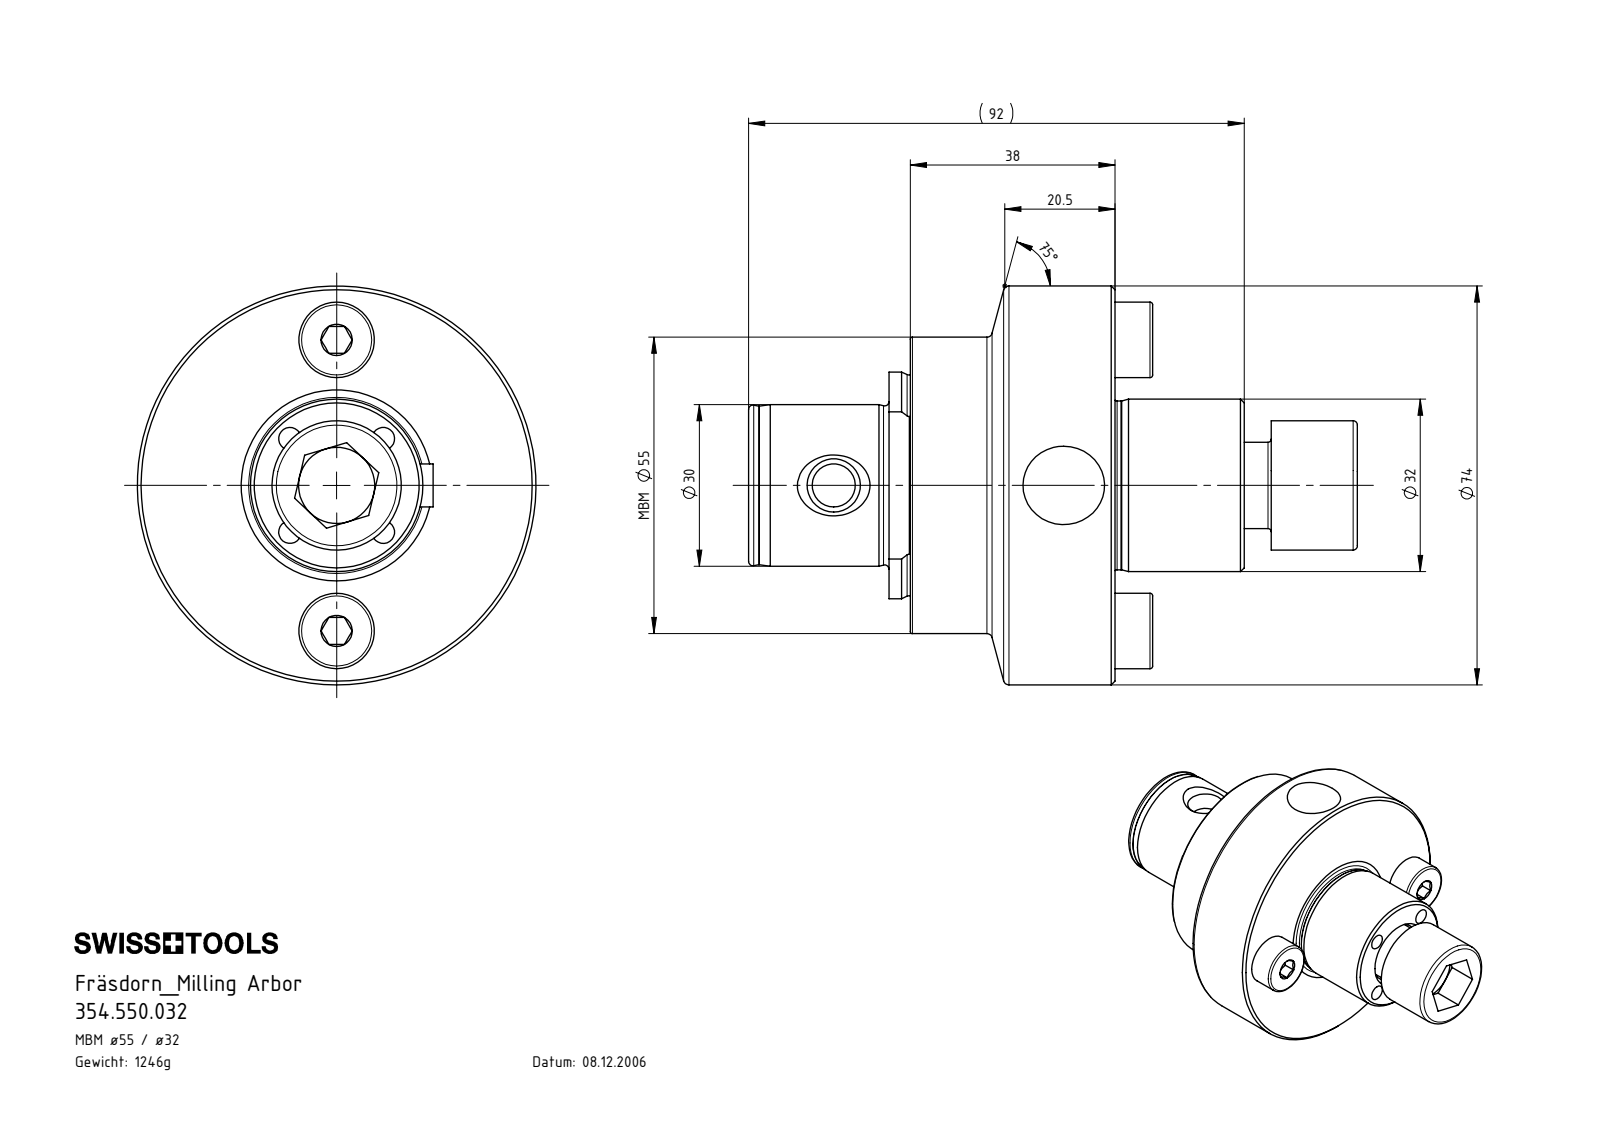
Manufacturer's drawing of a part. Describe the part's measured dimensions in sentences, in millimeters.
The part is named "D32-ER2.002.014_A; D32-ER1.K62.010_A; D32-ER1.K61.024; 354.550.032 (+2 more)". Its 3-D file was written by "SolidWorks 2017 (CONFIG_CONTROL_DESIGN)". It is 5 solids with 267 faces: 42 planar, 120 cylindrical and 105 other. Overall it measures 109 by 74 by 73.92 millimeters. Its volume is 173 025 cubic millimeters and its surface area 39 016 square millimeters. Round holes: 12 of diameter 3, 4 of diameter 5, 1 of diameter 6.5, 1 of diameter 8, 1 of diameter 11, 1 of diameter 14, 1 of diameter 17, 1 of diameter 23. Round bosses or shafts: 1 of diameter 74, 1 of diameter 55, 1 of diameter 42, 1 of diameter 32, 1 of diameter 31.3, 1 of diameter 30, 1 of diameter 24, 1 of diameter 16. Partial cylindrical surfaces (rounded edges, fillets, slot ends): 2 of radius 4, 1 of radius 7, 1 of radius 21.02. The main face-to-face distances are 10, 41, 31, 38, 69, 79, 14, 7, 24, 17. The hole center spacings are 14.5, 25.11, 2.98, 11.82, 12.25, 15.14, 22.16, 24.1.
